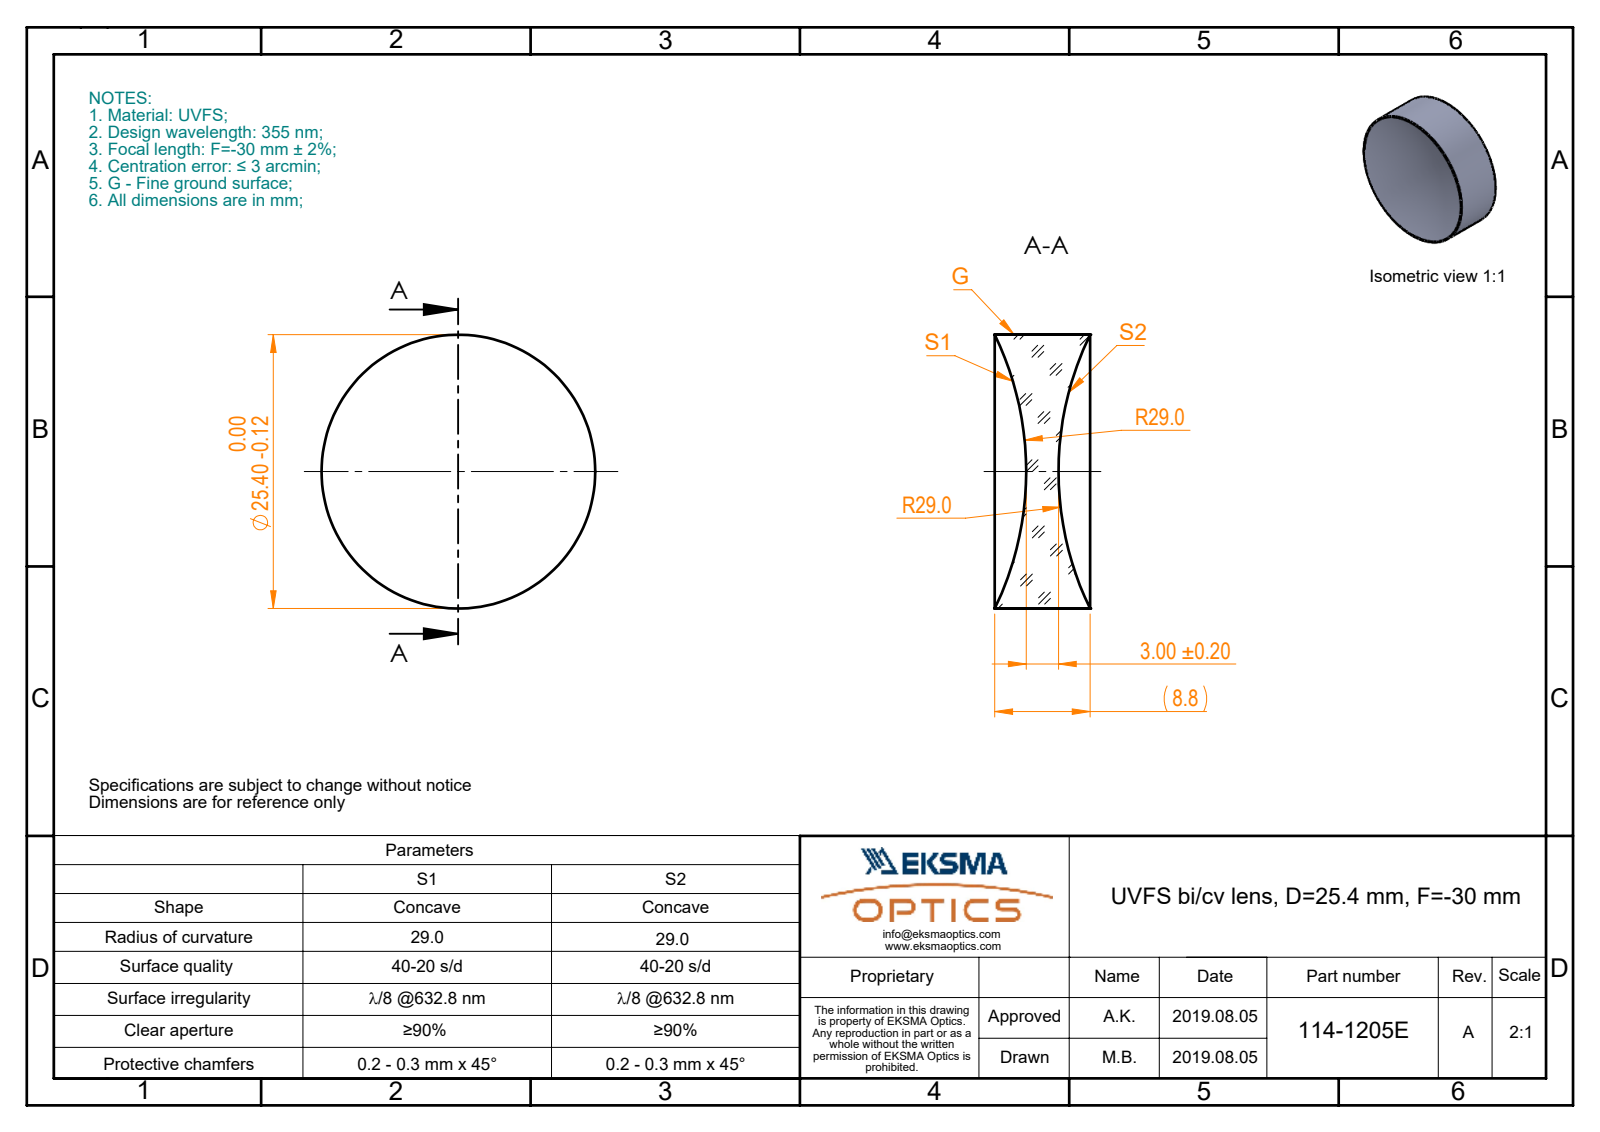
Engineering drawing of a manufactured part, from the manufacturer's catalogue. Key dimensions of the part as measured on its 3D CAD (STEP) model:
Part name (STEP PRODUCT): 114-1205E UVFS bi-cv 25.4 F-30
STEP written by: SolidWorks 2017 (CONFIG_CONTROL_DESIGN)
Units: millimetres
Bodies: 1 solid, 6 faces (0 planar, 2 cylindrical, 4 other)
Overall size (bounding box): 25.4 × 25.4 × 8.85
Volume: 2 976 mm³ · Surface area: 1 773 mm²
Round bosses / shafts (diameter × count): ⌀25.4 ×1
